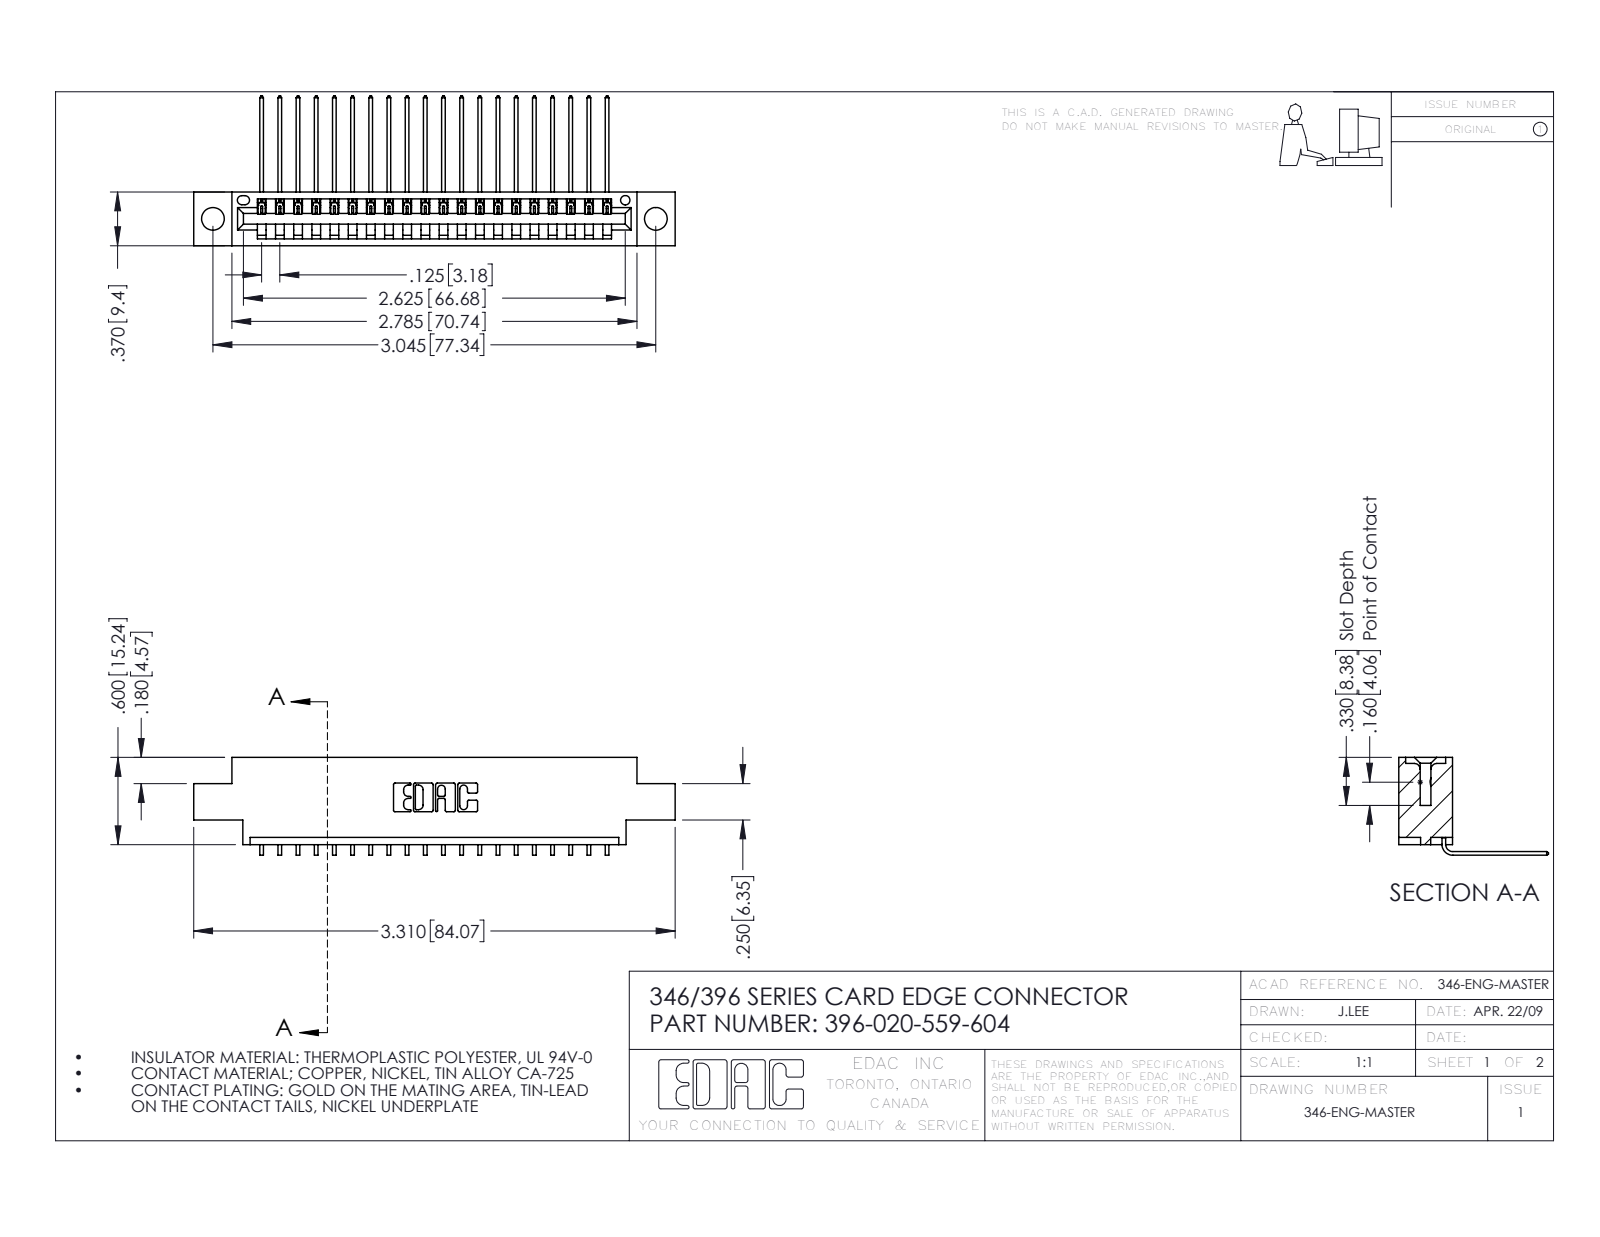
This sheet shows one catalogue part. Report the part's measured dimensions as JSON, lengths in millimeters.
{"part_name": "345-292-001_558 559 Tail - 1; 346 Part_0.170 Offset - 0.156 Dia-TH; 396-020-559-604", "step_written_by": "SolidWorks 2016 (CONFIG_CONTROL_DESIGN)", "units": "millimeters", "bodies": {"solids": 21, "faces": 1326, "planar": 920, "cylindrical": 406, "other": 0}, "overall_size": [84.1, 26.2, 17.1], "volume_mm3": 7720, "surface_area_mm2": 9774, "round_holes": [[4, 2], [1.6, 1]], "partial_cylinders_radius": [[0.2, 40], [0.3, 22], [0.2, 6], [0.8, 6], [0.7, 3], [0.8, 2], [1, 2], [0.4, 1]], "face_to_face_distances": [1.2, 9.4, 8.2, 6.4, 0.6, 1.8, 3.8, 5.6, 2.5, 4.4], "hole_center_spacings": [6.2, 72.1, 77.3]}
